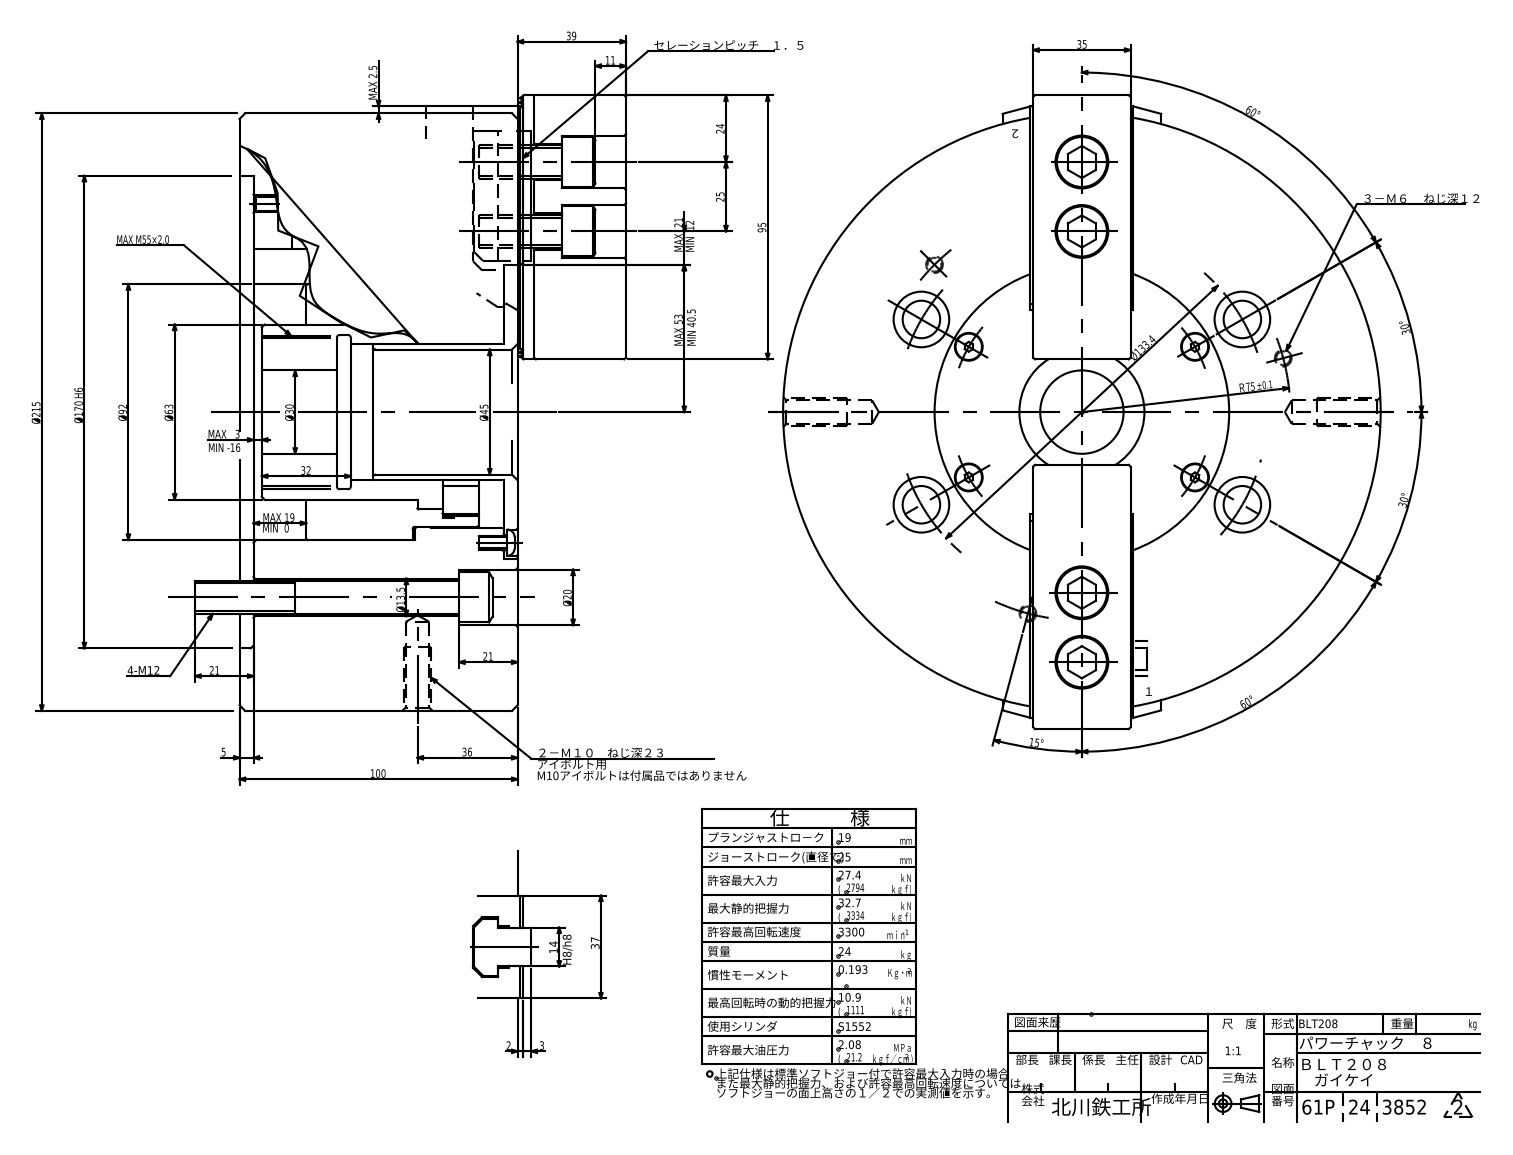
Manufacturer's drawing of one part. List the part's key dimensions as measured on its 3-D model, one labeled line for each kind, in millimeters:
Part name (STEP PRODUCT): BLT208-Solid
STEP written by: ST-DEVELOPER v16.7 (AUTOMOTIVE_DESIGN)
Units: millimetres
Bodies: 1 solid, 2125 faces (1504 planar, 467 cylindrical, 154 other)
Overall size (bounding box): 215 × 215 × 155.2
Volume: 3 447 000 mm³ · Surface area: 294 902 mm²
Round holes (diameter × count): ⌀4.2 ×4, ⌀5.5 ×4, ⌀10 ×4, ⌀10.3 ×4, ⌀13 ×4, ⌀13.5 ×4, ⌀19 ×4, ⌀20 ×4, ⌀5.2 ×3, ⌀8.5 ×1, ⌀30 ×1, ⌀45 ×1
Round bosses / shafts (diameter × count): ⌀18 ×8, ⌀11.7 ×8, ⌀9.5 ×4, ⌀4.83 ×4, ⌀215 ×1, ⌀83 ×1, ⌀75 ×1
Partial cylindrical surfaces — rounded edges, fillets, slot ends (radius × count): R0.1 ×78, R0.8 ×4, R5 ×2, R7.5 ×2, R10.75 ×2, R0.51 ×1, R2.19 ×1, R4.08 ×1
Main face-to-face distances: 95, 5, 100, 39.2, 35, 9.5, 11, 139.2, 134.2, 85.5
Hole centre spacings: 47, 66.7, 19.7, 53.68, 59.35, 63, 72.5, 76.49
